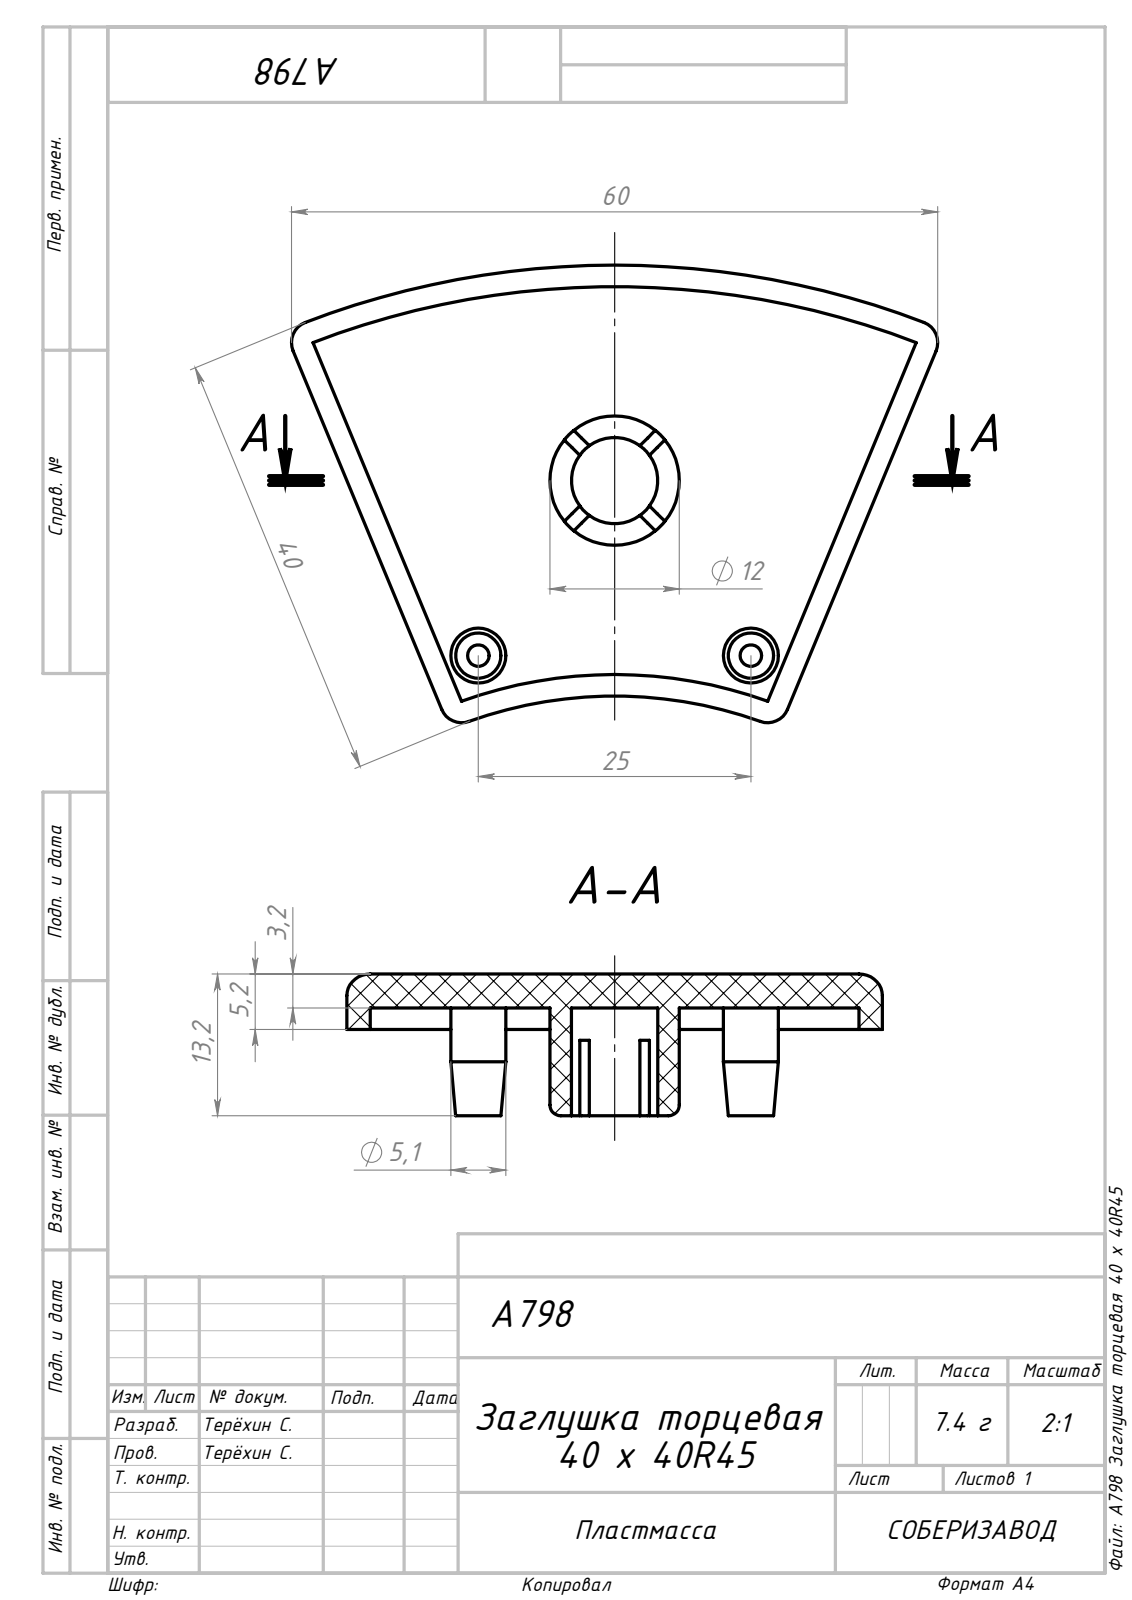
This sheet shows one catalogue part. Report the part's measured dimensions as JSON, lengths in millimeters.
{"part_name": "A798 Заглушка торцевая 40 х 40R45", "step_written_by": "SolidWorks 2022 (AUTOMOTIVE_DESIGN)", "units": "millimeters", "bodies": {"solids": 1, "faces": 67, "planar": 28, "cylindrical": 23, "other": 16}, "overall_size": [59.95, 42.47, 13.15], "volume_mm3": 7300, "surface_area_mm2": 5883, "round_holes": [[2, 2], [8, 1]], "round_bosses_or_shafts": [[5.1, 2], [12, 1]], "partial_cylinders_radius": [[2, 6], [39.96, 1], [41.96, 1], [77.96, 1], [79.96, 1]], "face_to_face_distances": [3.15, 2, 5.15, 2.01, 1.24, 8, 10, 13.15, 7, 1], "hole_center_spacings": [20.58, 25.28]}
